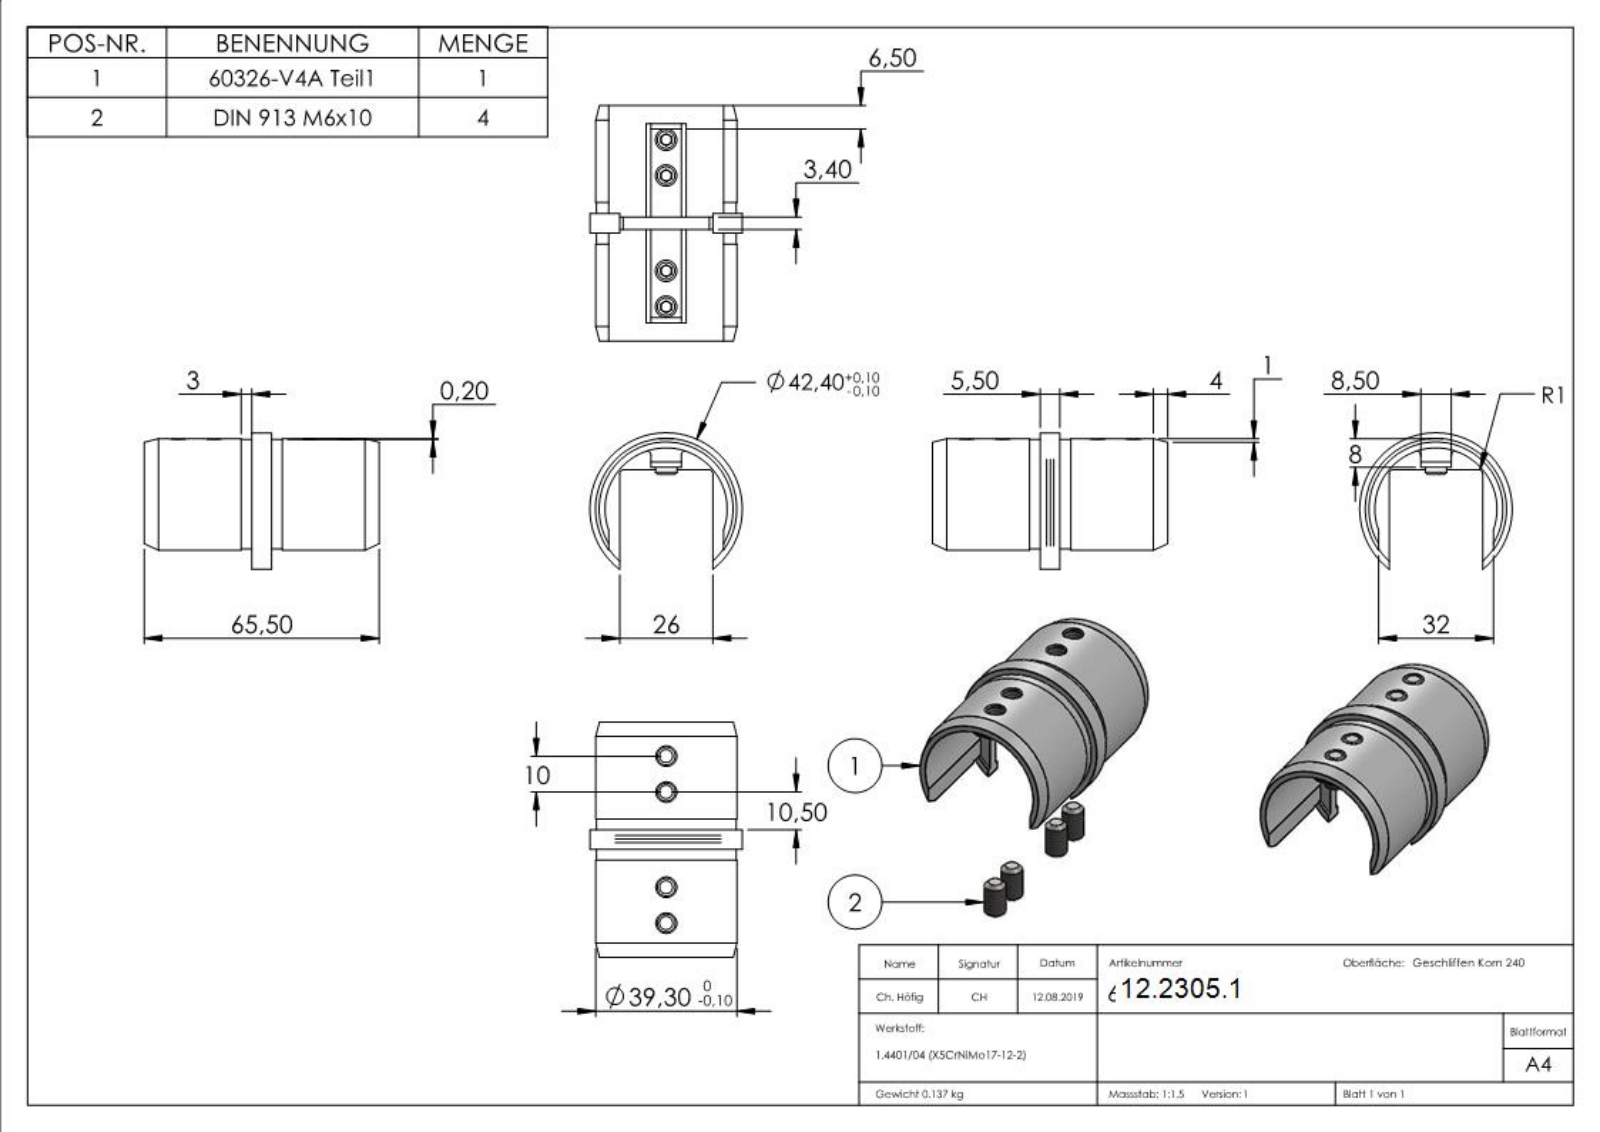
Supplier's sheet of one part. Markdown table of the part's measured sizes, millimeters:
| quantity | value |
| --- | --- |
| part name | 6032X-240 Teil1_60326-V4A Teil1; 60326-V4A; DIN913_DIN 913 M6x10 |
| STEP written by | SolidWorks 2015 (CONFIG_CONTROL_DESIGN) |
| units | millimeters |
| bodies | 5 solids, 388 faces (210 planar, 45 cylindrical, 133 other) |
| overall size | 65.5 × 42.4 × 37.95 |
| volume | 17 130 mm³ |
| surface area | 13 654 mm² |
| round holes (diameter × count) | 5 × 4 |
| round bosses / shafts (diameter × count) | 6 × 4 |
| partial cylindrical surfaces (radius × count) | 1 × 4, 17 × 1, 19.45 × 1, 19.65 × 1, 21.2 × 1 |
| main face-to-face distances | 11.75, 20.25, 1.05, 4.45, 32, 3, 30, 31.05, 34.45, 35.5 |
| hole center spacings | 10, 36.5, 26.5, 46.5 |
